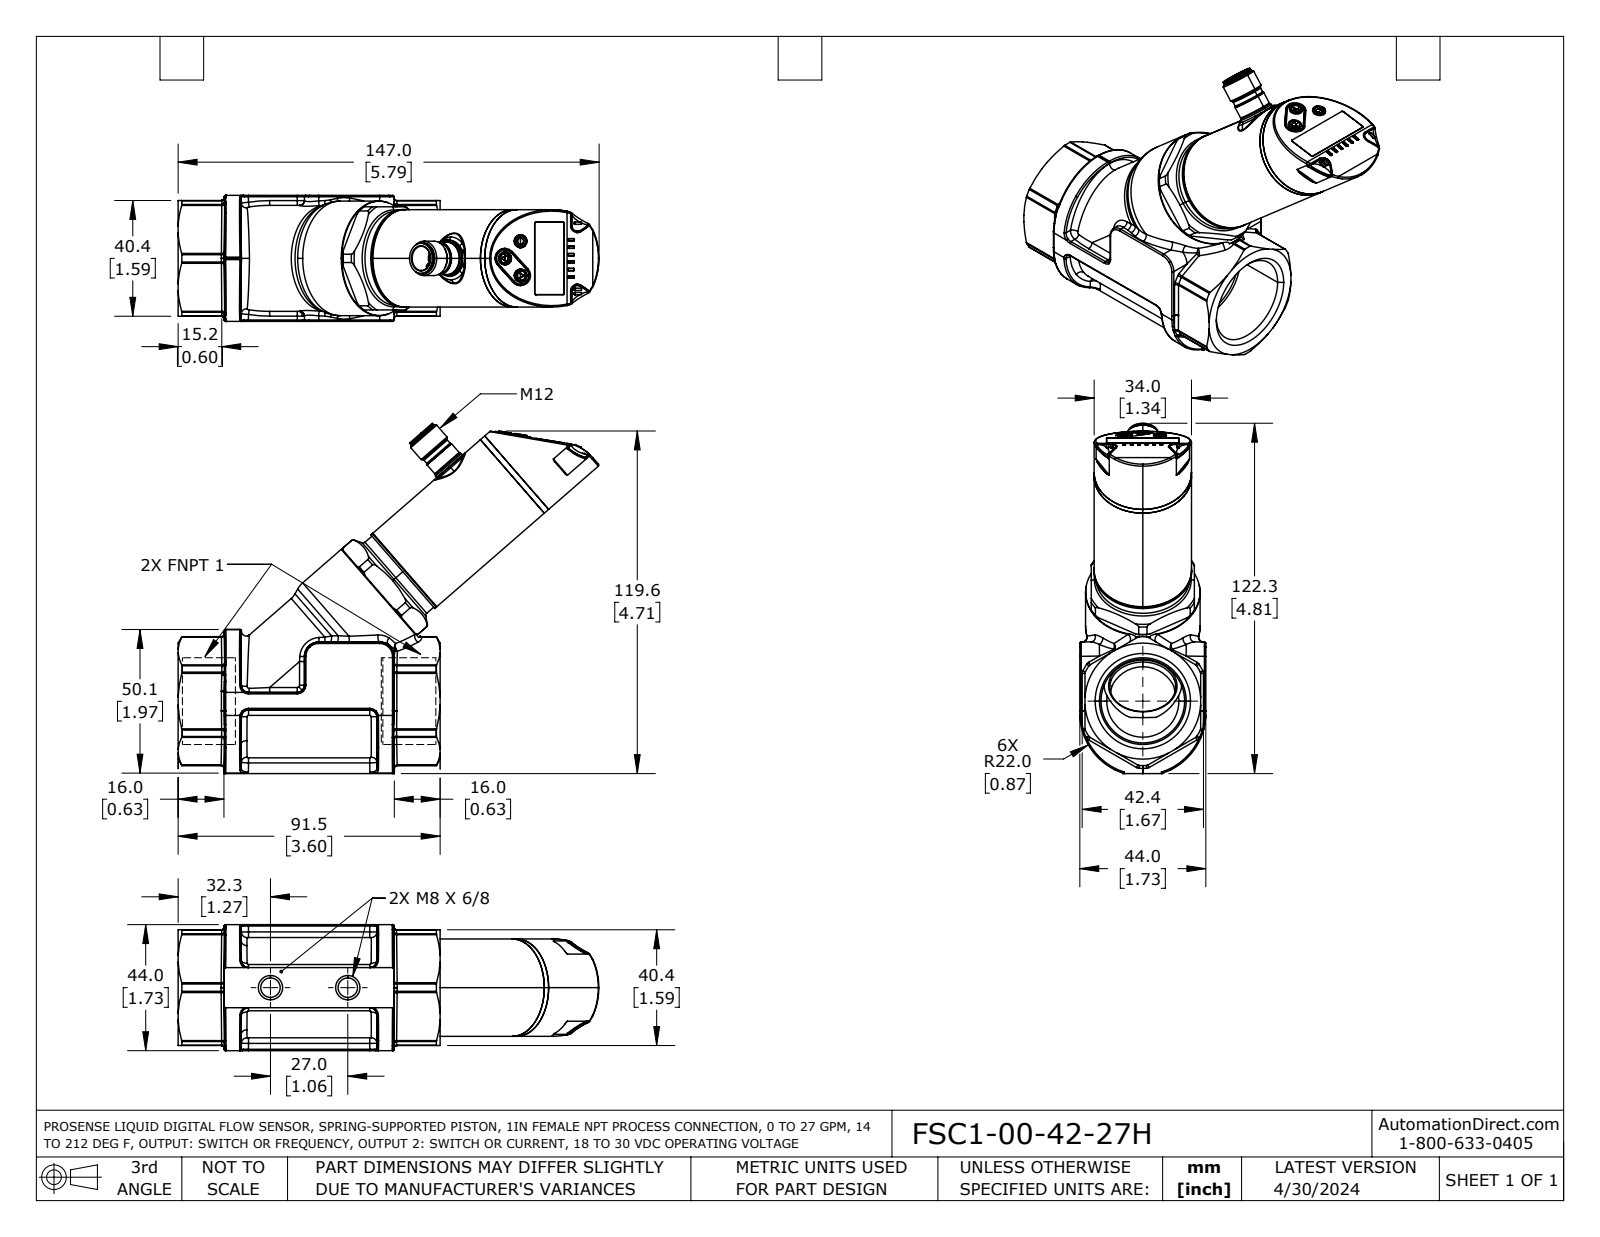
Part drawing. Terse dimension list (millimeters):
name: FSC1-00-42-27H
written by: SolidWorks 2021 (AUTOMOTIVE_DESIGN)
unit: mm
bodies: 14 solids, 2242 faces (592 planar, 798 cylindrical, 852 other)
size: 146.9 × 122.3 × 44
volume: 113 800 mm³; area: 61 450 mm²
holes: 3× ⌀0.8, 3× ⌀4.5, 2× ⌀1, 2× ⌀2, 2× ⌀6.8, 1× ⌀1.4, 1× ⌀2.2, 1× ⌀3.5, 1× ⌀8.5, 1× ⌀10, 1× ⌀12.2, 1× ⌀16.4
bosses: 3× ⌀4.4, 3× ⌀2.5, 1× ⌀40, 1× ⌀34.1, 1× ⌀34, 1× ⌀33.2, 1× ⌀33.1, 1× ⌀32.9
rounds: 84× R0.2, 73× R0.1, 51× R0.5, 47× R1, 17× R2, 15× R0.4, 12× R2.5, 9× R15
face distances: 40.4, 1.8, 42.2, 0.5, 91.5, 1.3, 41.7, 43.5, 13, 29
hole spacings: 8.1, 12, 12.2, 8.1, 8.2, 12.2, 8.4, 12.2
